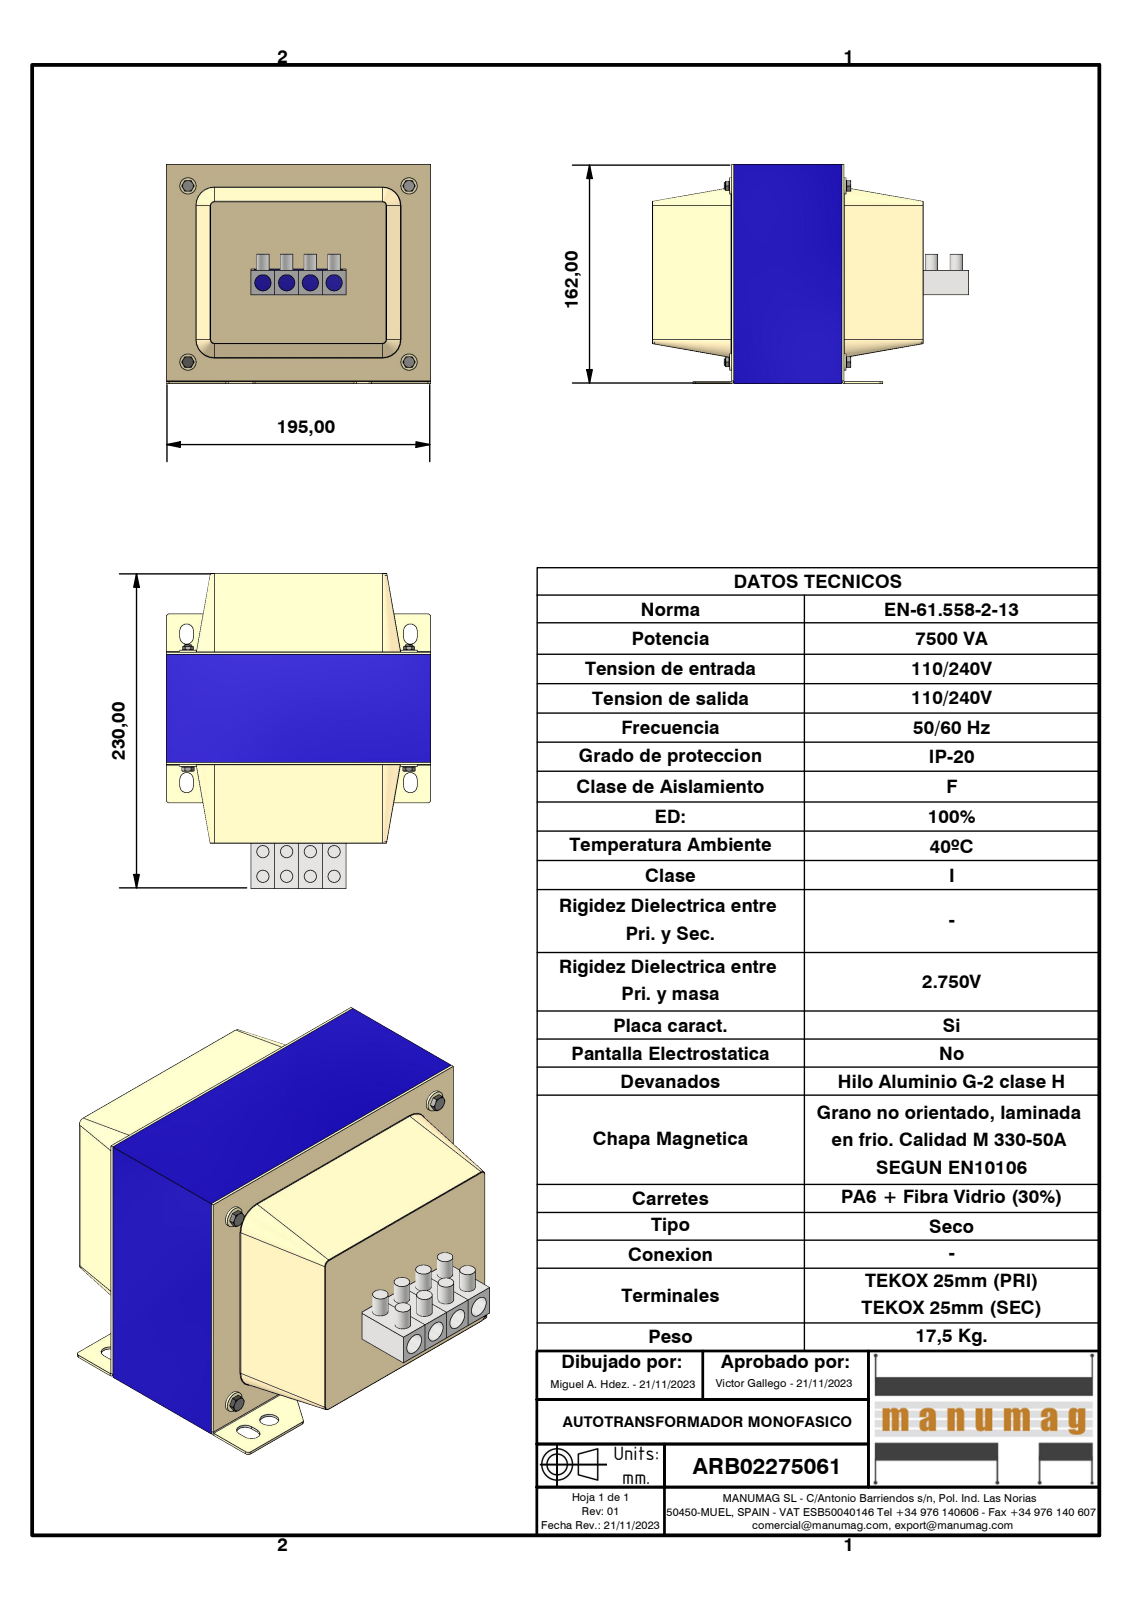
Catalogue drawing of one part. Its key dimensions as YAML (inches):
part_name: "ARB02275061; EI195 x 162 - 80 (Rc65) Azul; TAPA RC65 CIEGA; TAPA RC65 VENTANA 4 ELEMENTOS 25 (+5 more)"
step_written_by: "Autodesk Inventor 2023 (AUTOMOTIVE_DESIGN)"
units: inches
bodies: {solids: 23, faces: 402, planar: 202, cylindrical: 112, other: 88}
overall_size: [9.193, 7.677, 6.378]
volume: 130
surface_area: 656.6
round_holes:
  - {diameter: 0.433, count: 8}
  - {diameter: 0.128, count: 4}
  - {diameter: 0.197, count: 4}
  - {diameter: 0.354, count: 4}
  - {diameter: 0.472, count: 4}
round_bosses_or_shafts:
  - {diameter: 0.354, count: 8}
  - {diameter: 0.472, count: 4}
  - {diameter: 0.264, count: 4}
  - {diameter: 0.232, count: 4}
  - {diameter: 0.18, count: 4}
partial_cylinders:
  - {radius: 0.015, count: 16}
  - {radius: 0.079, count: 14}
  - {radius: 0.197, count: 8}
  - {radius: 0.02, count: 2}
face_to_face_distances: [0.059, 2.303, 5.512, 3.15, 5.118, 1.28, 5.453, 2.559, 2.362, 2.244]
hole_center_spacings: [0.689, 1.378, 3.168, 3.557, 3.675, 4.016, 4.234, 4.331]
